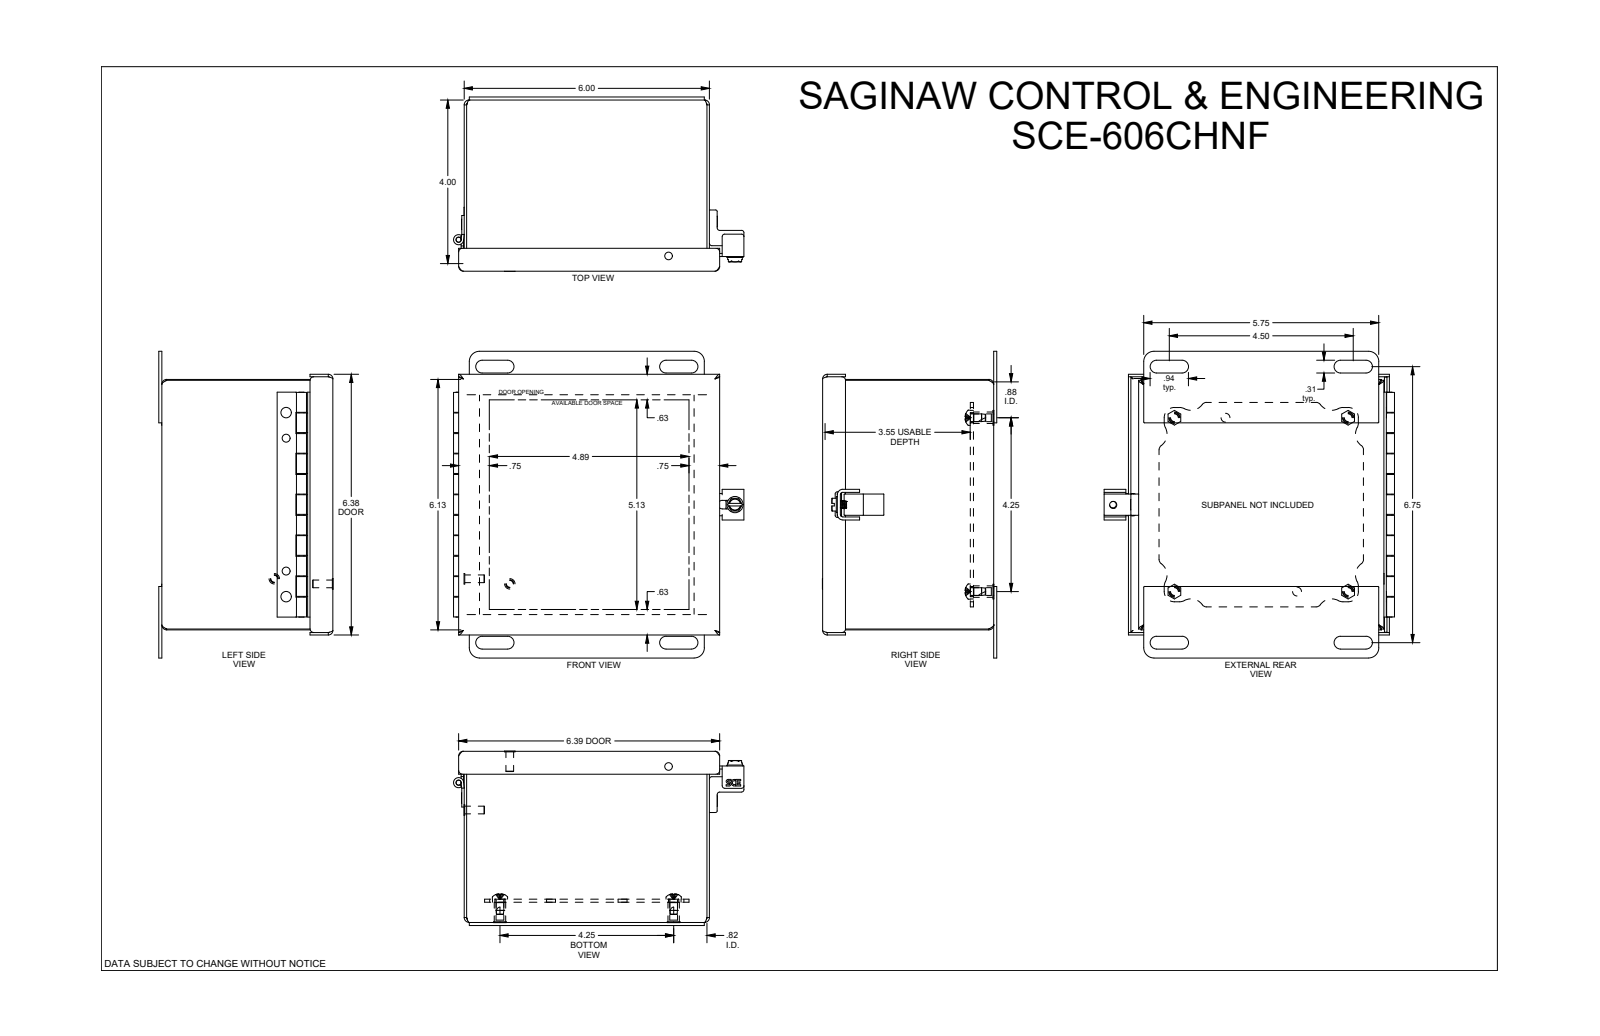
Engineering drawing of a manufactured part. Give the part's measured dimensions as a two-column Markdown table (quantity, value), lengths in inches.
| quantity | value |
| --- | --- |
| part name | SCE-606CHNF |
| STEP written by | SolidWorks 2019 (CONFIG_CONTROL_DESIGN) |
| units | inches |
| bodies | 0 solids, 1004 faces (463 planar, 273 cylindrical, 268 other) |
| overall size | 7.5 × 7.104 × 4.265 |
| round holes (diameter × count) | 0.19 × 7, 0.193 × 5, 0.25 × 4, 0.281 × 4, 0.193 × 2, 0.218 × 2, 0.126 × 1, 0.156 × 1, 0.187 × 1, 0.266 × 1 |
| round bosses / shafts (diameter × count) | 0.188 × 10, 0.256 × 5, 0.373 × 4, 0.28 × 4, 0.396 × 1, 0.246 × 1, 0.123 × 1 |
| partial cylindrical surfaces (radius × count) | 0.01 × 50, 0.25 × 16, 0.06 × 13, 0.052 × 8, 0.112 × 8, 0.125 × 8, 0.156 × 8, 0.344 × 8 |
| main face-to-face distances | 0.06, 5.94, 4.125, 6.065, 0.06, 4.185, 4.125, 4.065, 0.075, 6 |
| hole center spacings | 4.25, 1.25, 2.251, 3, 4.43, 5.202, 6.01, 0.305 |
